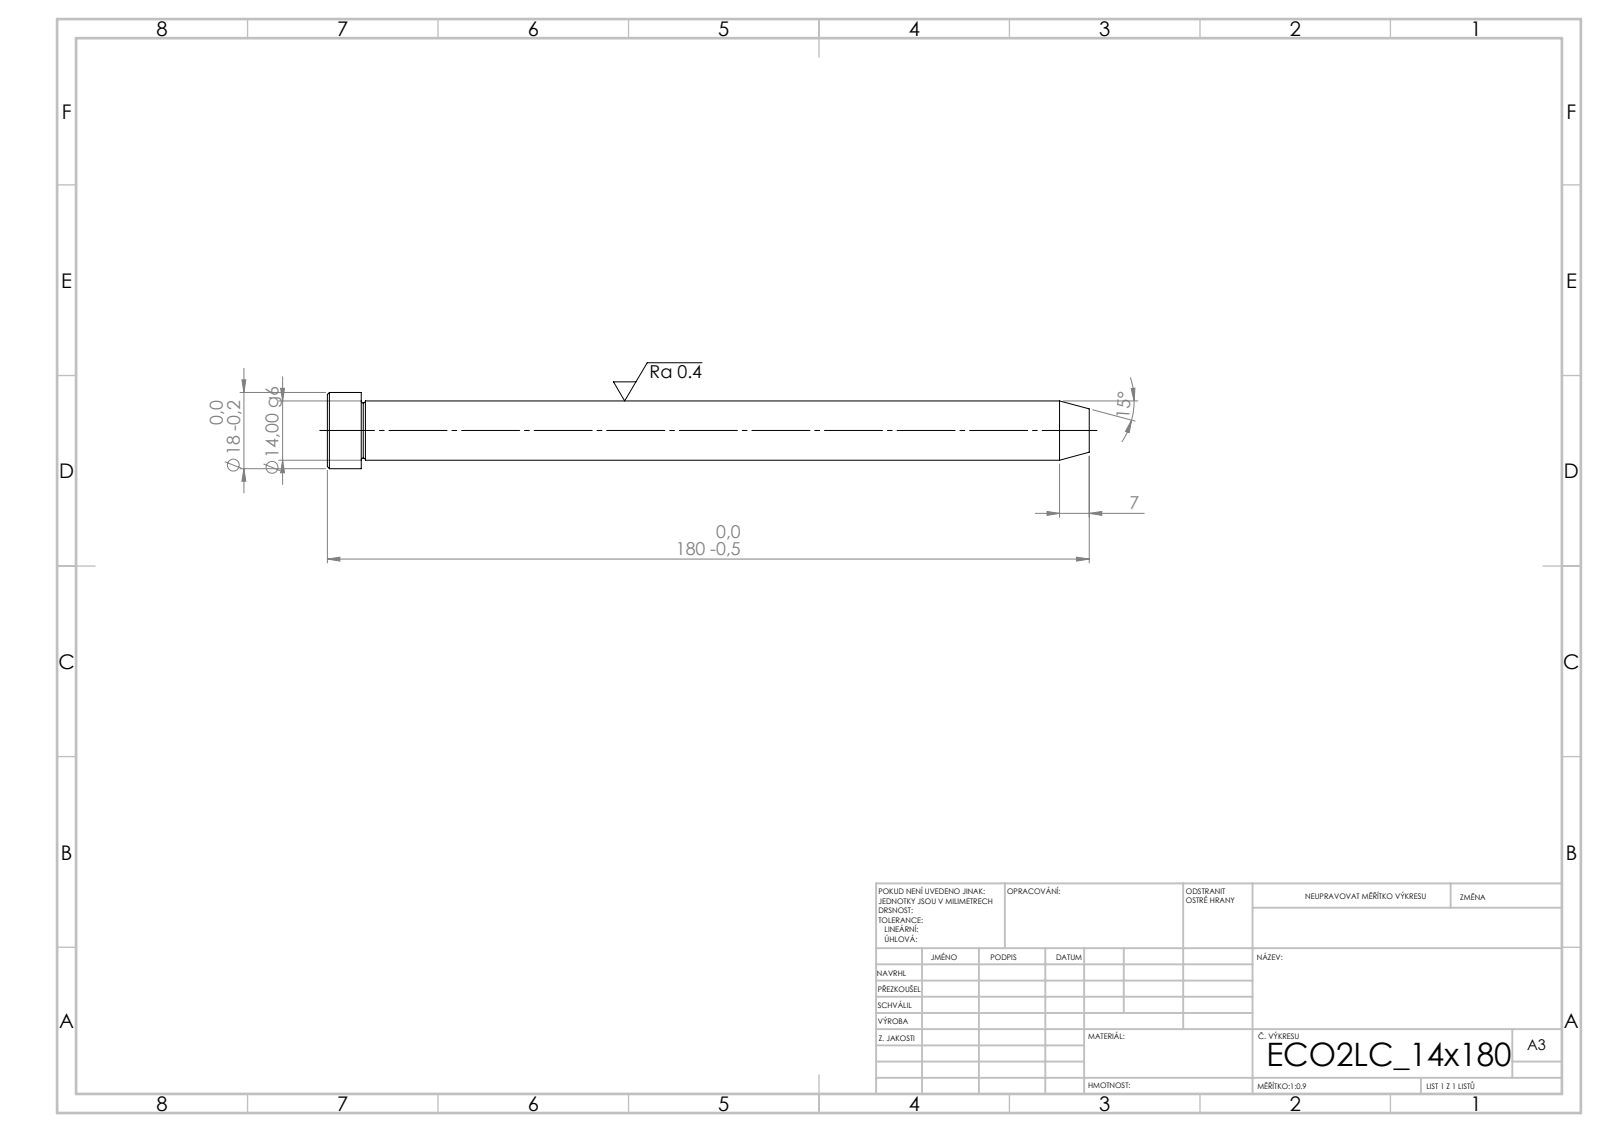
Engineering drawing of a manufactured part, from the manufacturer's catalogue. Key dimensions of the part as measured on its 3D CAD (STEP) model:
STEP written by: SolidWorks 2019 (CONFIG_CONTROL_DESIGN)
Units: millimetres
Bodies: 1 solid, 15 faces (3 planar, 4 cylindrical, 8 other)
Overall size (bounding box): 180 × 18 × 18
Volume: 28 226 mm³ · Surface area: 8 428 mm²
Round bosses / shafts (diameter × count): ⌀18 ×1, ⌀14 ×1
Main face-to-face distances: 8, 172, 180
